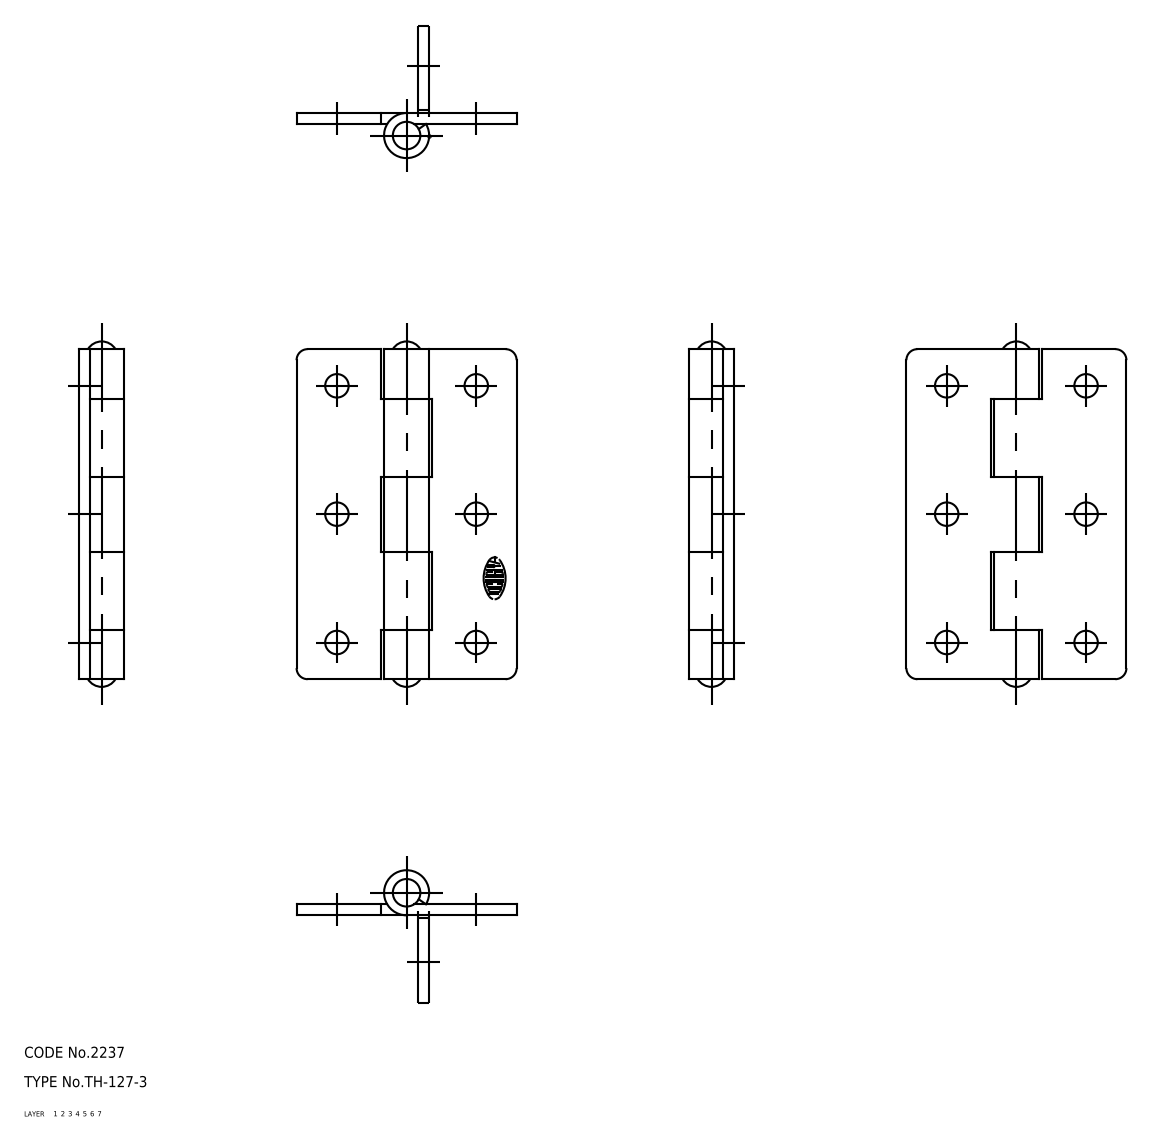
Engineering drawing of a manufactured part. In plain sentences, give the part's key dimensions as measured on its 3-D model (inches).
The part is named "hinge piece_B; hinge piece_A; shaft; TH_127_3_2913_36". Its 3-D file was written by "CADfix (AUTOMOTIVE_DESIGN)". It is 3 solids with 60 faces: 0 planar, 0 cylindrical and 60 other. Overall it measures 3.709 by 2.362 by 0.484 inches. Its volume is 1.4 cubic inches and its surface area 27.92 square inches.
